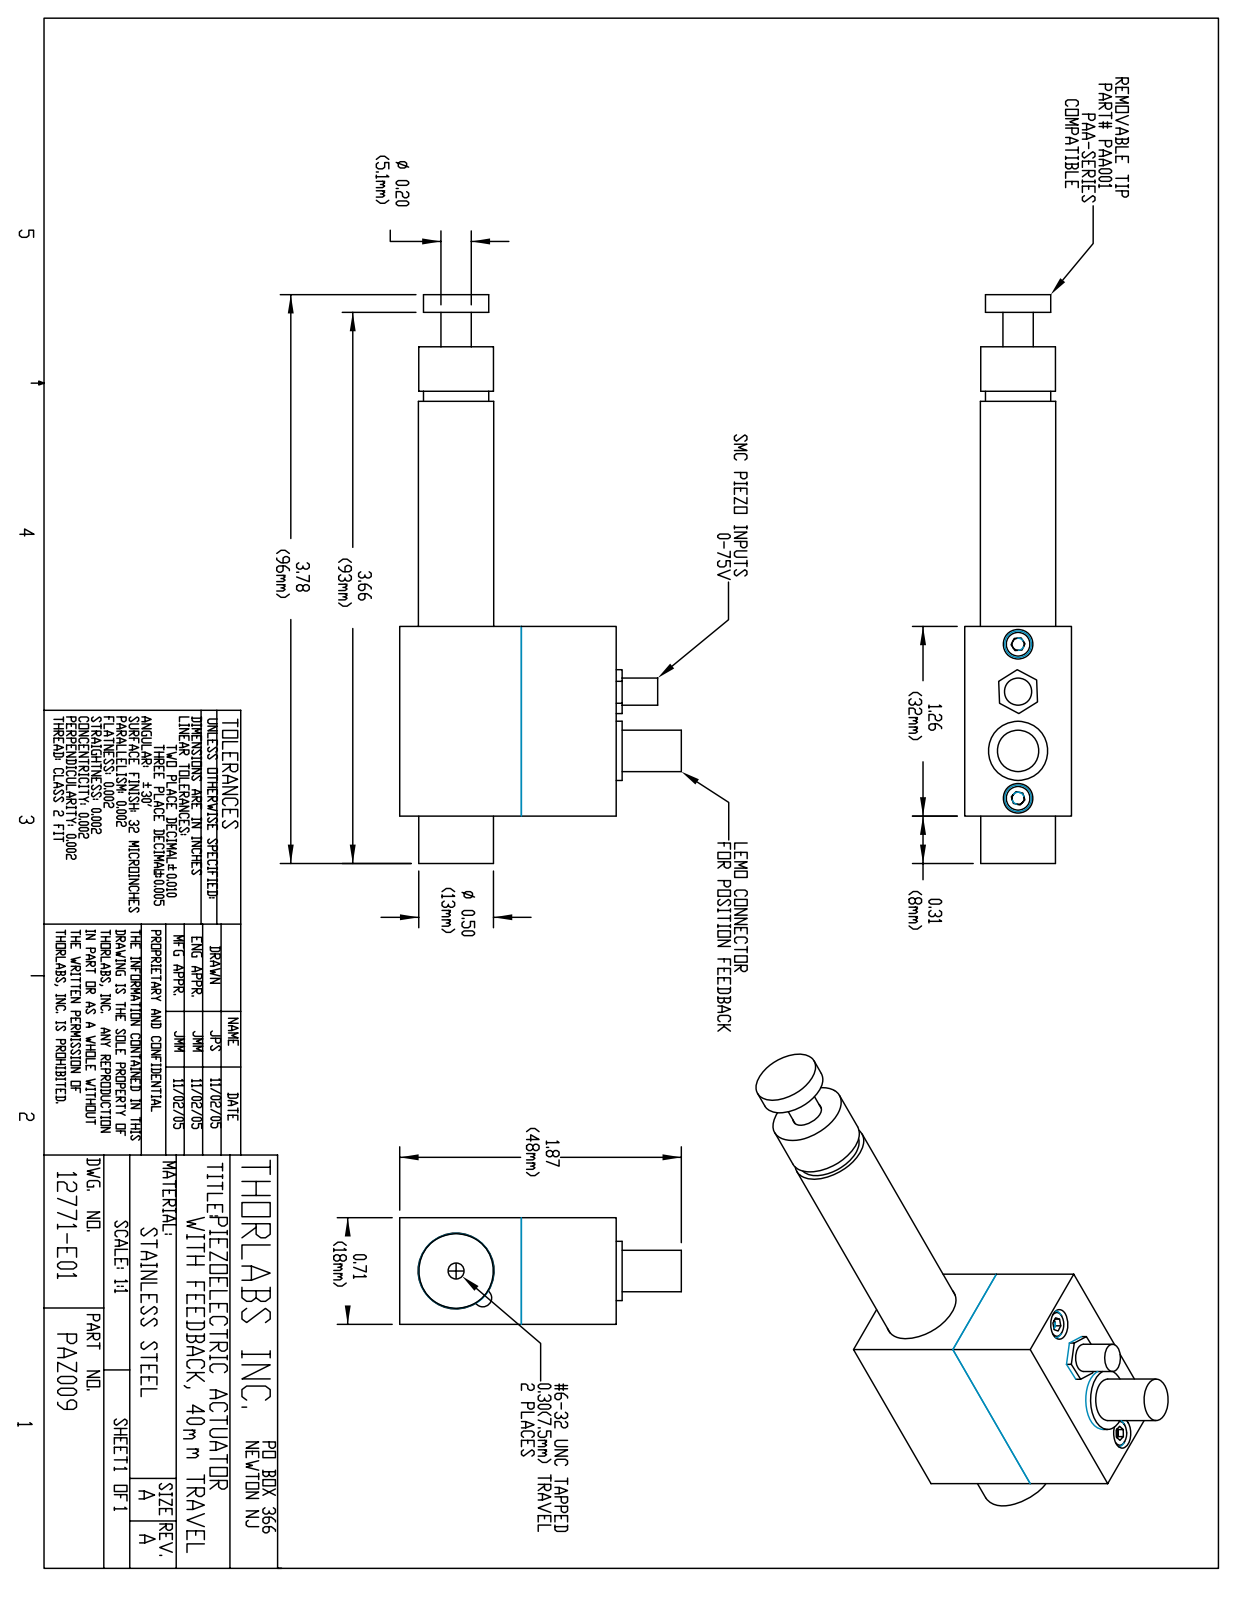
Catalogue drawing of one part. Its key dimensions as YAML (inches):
part_name: "12771-E0W"
step_written_by: "SolidWorks 2007 (AUTOMOTIVE_DESIGN)"
units: inches
bodies: {solids: 0, faces: 110, planar: 60, cylindrical: 38, other: 12}
overall_size: [3.78, 1.87, 0.709]
round_holes:
  - {diameter: 0.098, count: 2}
  - {diameter: 0.197, count: 2}
  - {diameter: 0.107, count: 1}
  - {diameter: 0.209, count: 1}
  - {diameter: 0.449, count: 1}
  - {diameter: 0.504, count: 1}
round_bosses_or_shafts:
  - {diameter: 0.5, count: 1}
  - {diameter: 0.496, count: 1}
  - {diameter: 0.433, count: 1}
  - {diameter: 0.394, count: 1}
  - {diameter: 0.276, count: 1}
  - {diameter: 0.201, count: 1}
  - {diameter: 0.181, count: 1}
partial_cylinders:
  - {radius: 0.059, count: 1}
face_to_face_distances: [0.709, 1.26, 1.437, 1.575, 0.315, 1.858, 3.118, 3.433, 0.346, 2.205]
hole_center_spacings: [1.024]
